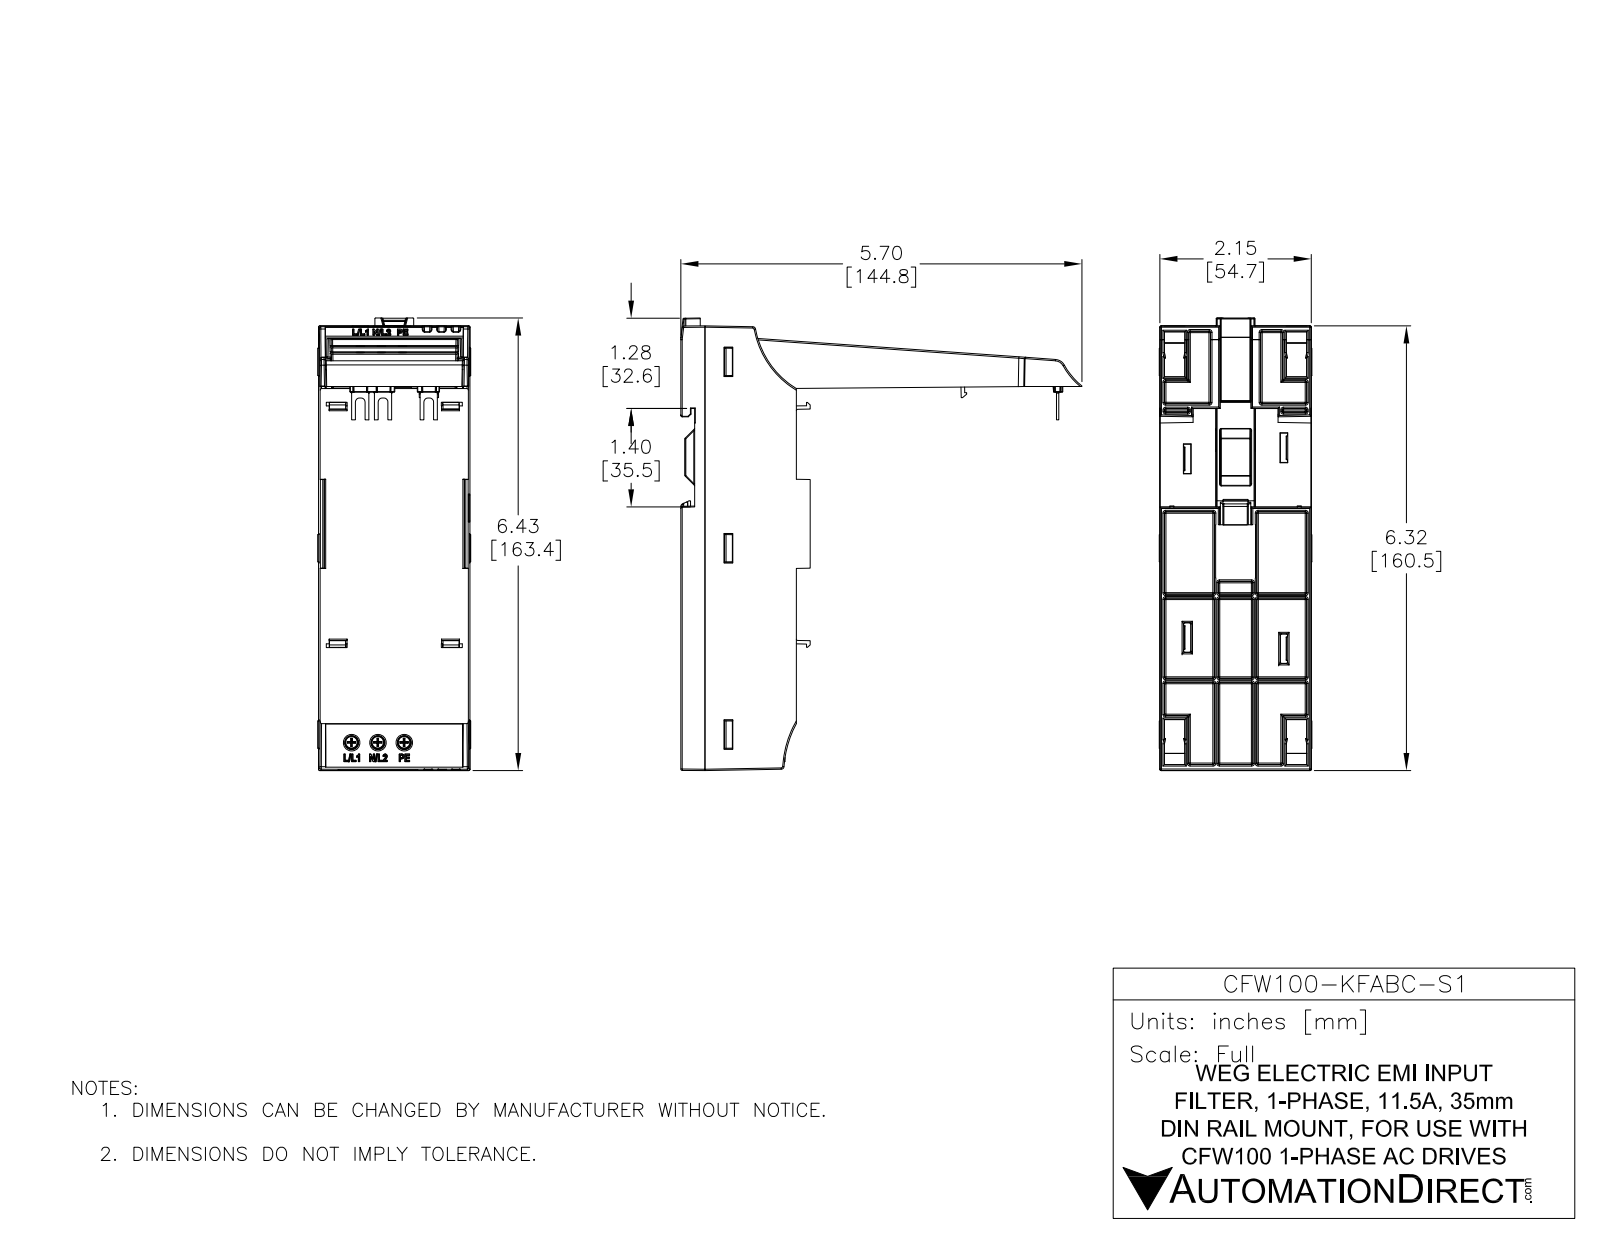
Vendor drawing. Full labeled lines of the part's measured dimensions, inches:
Part name (STEP PRODUCT): CFW100 FILTER
STEP written by: SolidWorks 2017 (AUTOMOTIVE_DESIGN)
Units: inches
Bodies: 1 solid, 58 faces (51 planar, 7 cylindrical, 0 other)
Overall size (bounding box): 6.319 × 5.702 × 2.152
Volume: 25.25 in³ · Surface area: 76.13 in²
Partial cylindrical surfaces — rounded edges, fillets, slot ends (radius × count): R0.039 ×1, R0.157 ×1, R1.26 ×1, R1.401 ×1, R2.562 ×1
Main face-to-face distances: 1.642, 2.152, 0.089, 2.063, 0.197, 1.445, 1.974, 0.868, 0.077, 2.065
